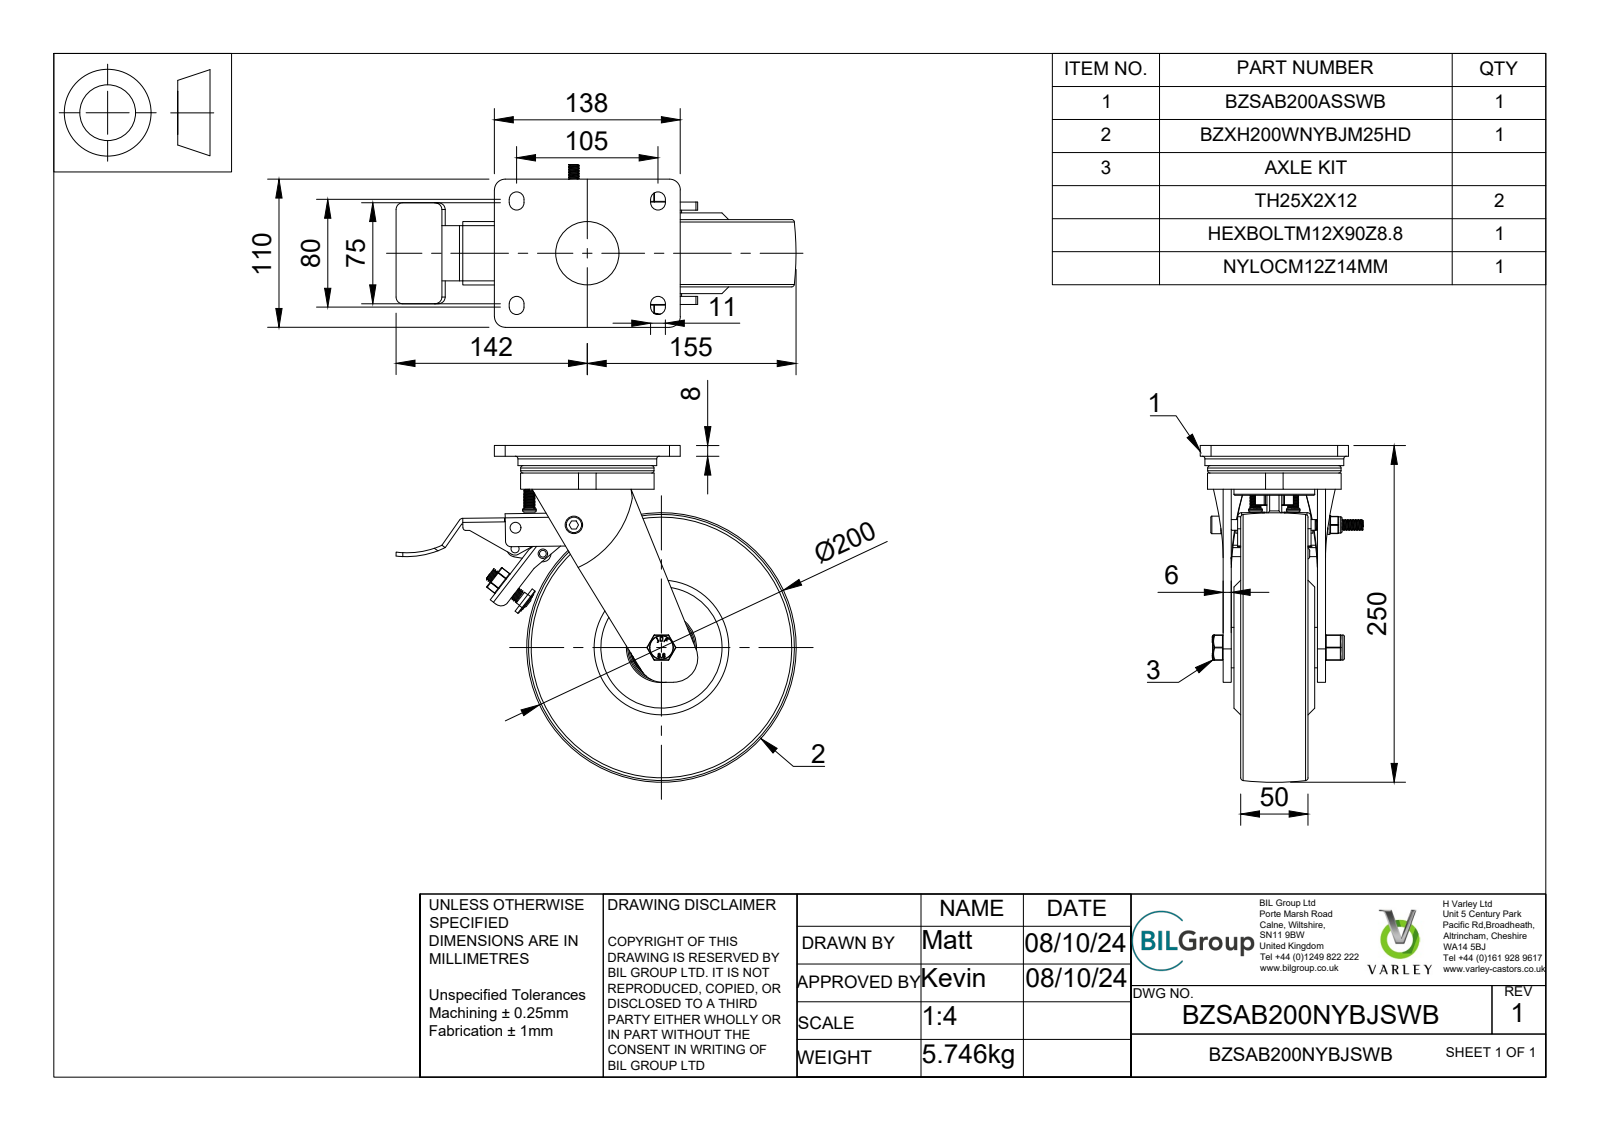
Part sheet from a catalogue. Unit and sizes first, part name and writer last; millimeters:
Units: millimetres
Overall size (bounding box): 297 × 250 × 120.83
Round holes (diameter × count): ⌀5 ×2, ⌀10 ×2, ⌀6 ×1, ⌀8 ×1, ⌀12 ×1, ⌀12.5 ×1, ⌀14 ×1, ⌀25 ×1, ⌀34.35 ×1, ⌀34.85 ×1, ⌀36.28 ×1, ⌀44.71 ×1
Round bosses / shafts (diameter × count): ⌀8 ×3, ⌀6 ×3, ⌀10 ×2, ⌀103 ×1, ⌀100 ×1, ⌀99 ×1, ⌀60 ×1, ⌀45.21 ×1
Partial cylindrical surfaces — rounded edges, fillets, slot ends (radius × count): R0.5 ×86, R1 ×8, R3 ×8, R5.5 ×8, R1.5 ×7, R2 ×7, R0.47 ×4, R0.9 ×4
Main face-to-face distances: 8, 50, 70, 7, 57, 6, 13, 63, 2, 3
Hole centre spacings: 15.62, 21.02, 28.04, 31.4, 43.44, 47.17, 111.83, 112.23
Volume: 2 067 000 mm³ · Surface area: 323 852 mm²
Bodies: 58 solids, 1042 faces (378 planar, 396 cylindrical, 268 other)
Part name (STEP PRODUCT): BZSAB200NYBJSWB v3; BZSAB200ASSWB v1; FABRICATED STEEL TOP PLATE; BEARING SEAL (+8 more)
STEP written by: Autodesk Translation Framework v13.20.0.188 (AUTOMOTIVE_DESIGN)
